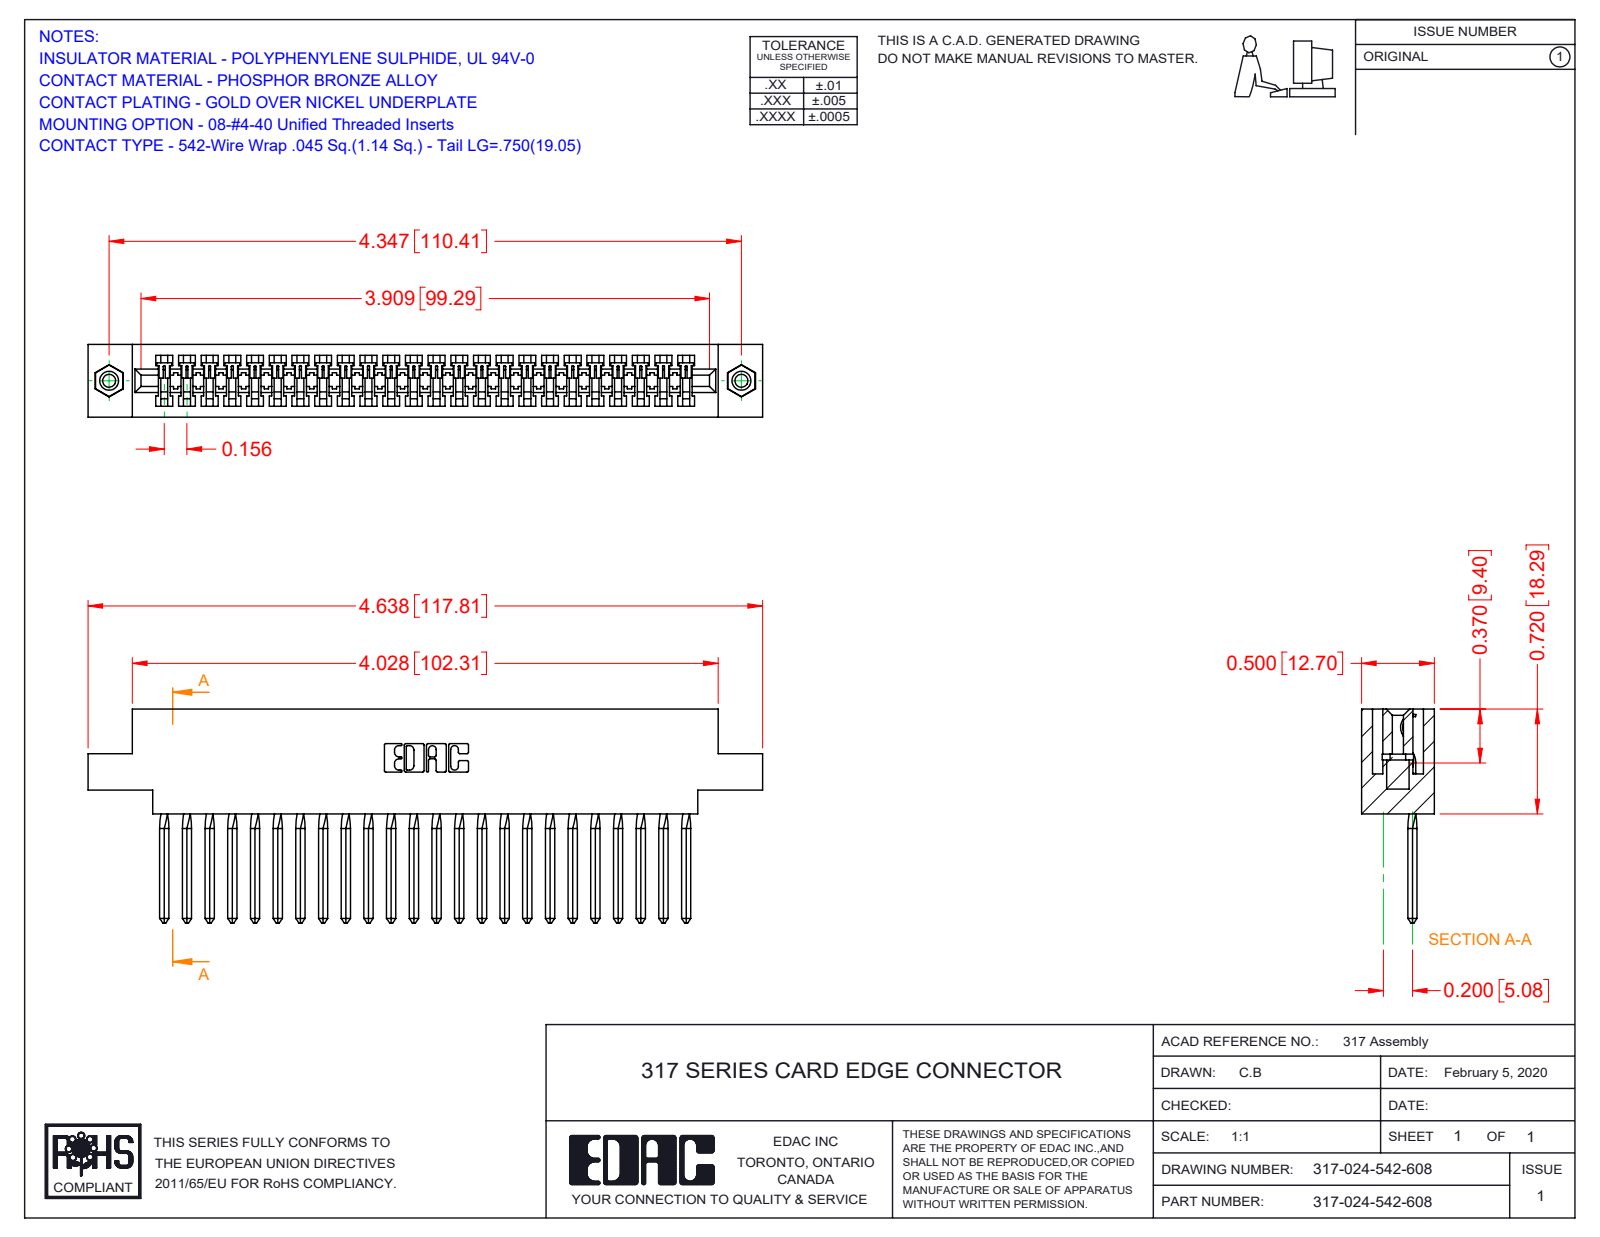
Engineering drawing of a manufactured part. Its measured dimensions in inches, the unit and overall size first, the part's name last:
Units: inches
Overall size (bounding box): 4.638 × 1.47 × 0.5
Round holes (diameter × count): ⌀0.089 ×2, ⌀0.125 ×2, ⌀0.156 ×2
Round bosses / shafts (diameter × count): ⌀0.155 ×2
Partial cylindrical surfaces — rounded edges, fillets, slot ends (radius × count): R0.006 ×48, R0.01 ×22, R0.007 ×6, R0.031 ×6, R0.026 ×3, R0.074 ×1, R0.089 ×1, R0.1 ×1
Main face-to-face distances: 0.5, 0.075, 0.425, 0.35, 0.11, 0.136, 0.72, 0.279, 0.211, 0.289
Hole centre spacings: 4.347
Volume: 1.081 in³ · Surface area: 32.9 in²
Bodies: 27 solids, 1962 faces (1626 planar, 224 cylindrical, 112 other)
Part name (STEP PRODUCT): 317-290-003_542; 317 Part_.156 Dia - TI; 317-024-542-678; 345-250-001_345-250-003-102
STEP written by: SolidWorks 2016 (CONFIG_CONTROL_DESIGN)
